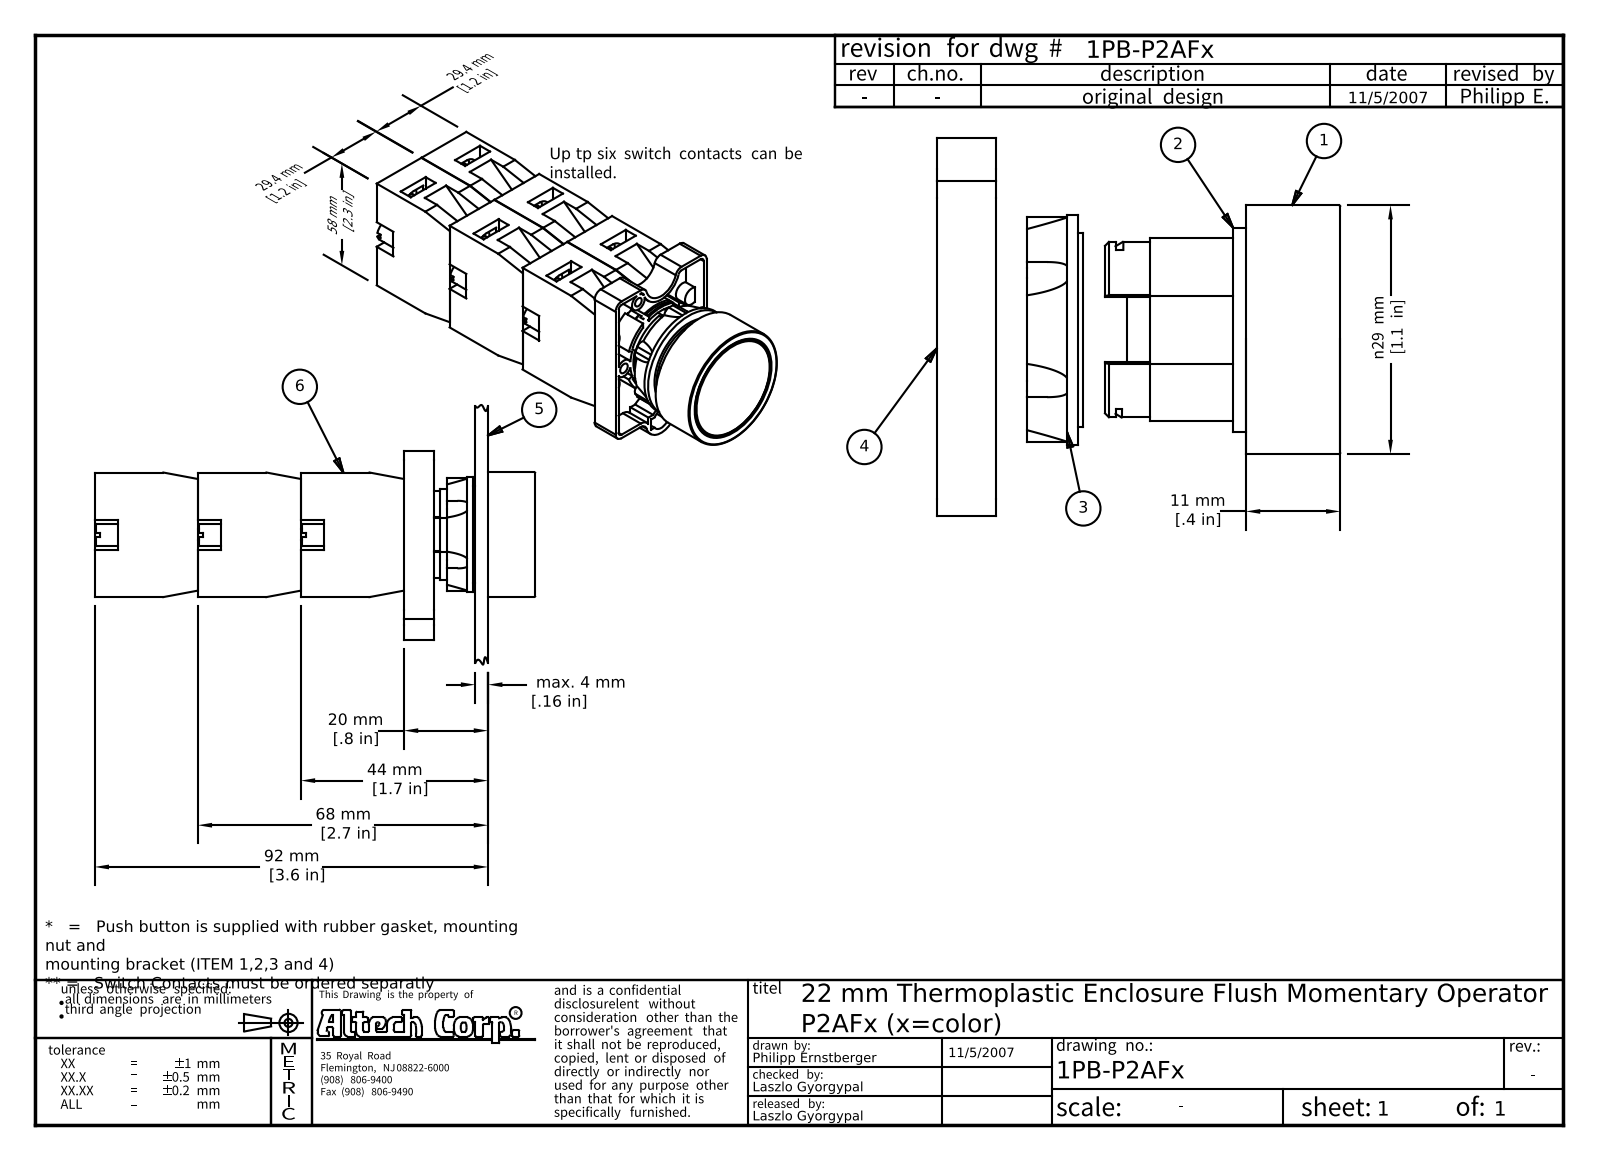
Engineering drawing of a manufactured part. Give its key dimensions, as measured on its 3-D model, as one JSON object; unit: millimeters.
{"part_name": "P2AFx_assembly; P2AFx_operator; P2AFx; 2PRG1 (+7 more)", "step_written_by": "Autodesk Inventor 2008 (AUTOMOTIVE_DESIGN)", "units": "millimeters", "bodies": {"solids": 29, "faces": 1168, "planar": 638, "cylindrical": 197, "other": 333}, "overall_size": [102.6, 60.45, 45], "volume_mm3": 71325, "surface_area_mm2": 45877, "round_holes": [[2.5, 6], [2.2, 2], [2.6, 2], [12, 1], [17.6, 1], [20.8, 1], [22.5, 1], [24.9, 1]], "round_bosses_or_shafts": [[3, 6], [2.75, 4], [1.5, 4], [5, 2], [4.2, 2], [29, 1], [26.8, 1], [24.5, 1]], "partial_cylinders_radius": [[1, 15], [1.5, 12], [2, 8], [2.25, 6], [3, 2], [3.3, 2], [5, 2], [2.6, 1]], "face_to_face_distances": [14.8, 14.7, 24, 3, 48, 29.5, 19.6, 29, 16.6, 64.6], "hole_center_spacings": [6.54, 26.07, 11.41, 12.25, 13, 14.51, 14.56, 17.17]}
